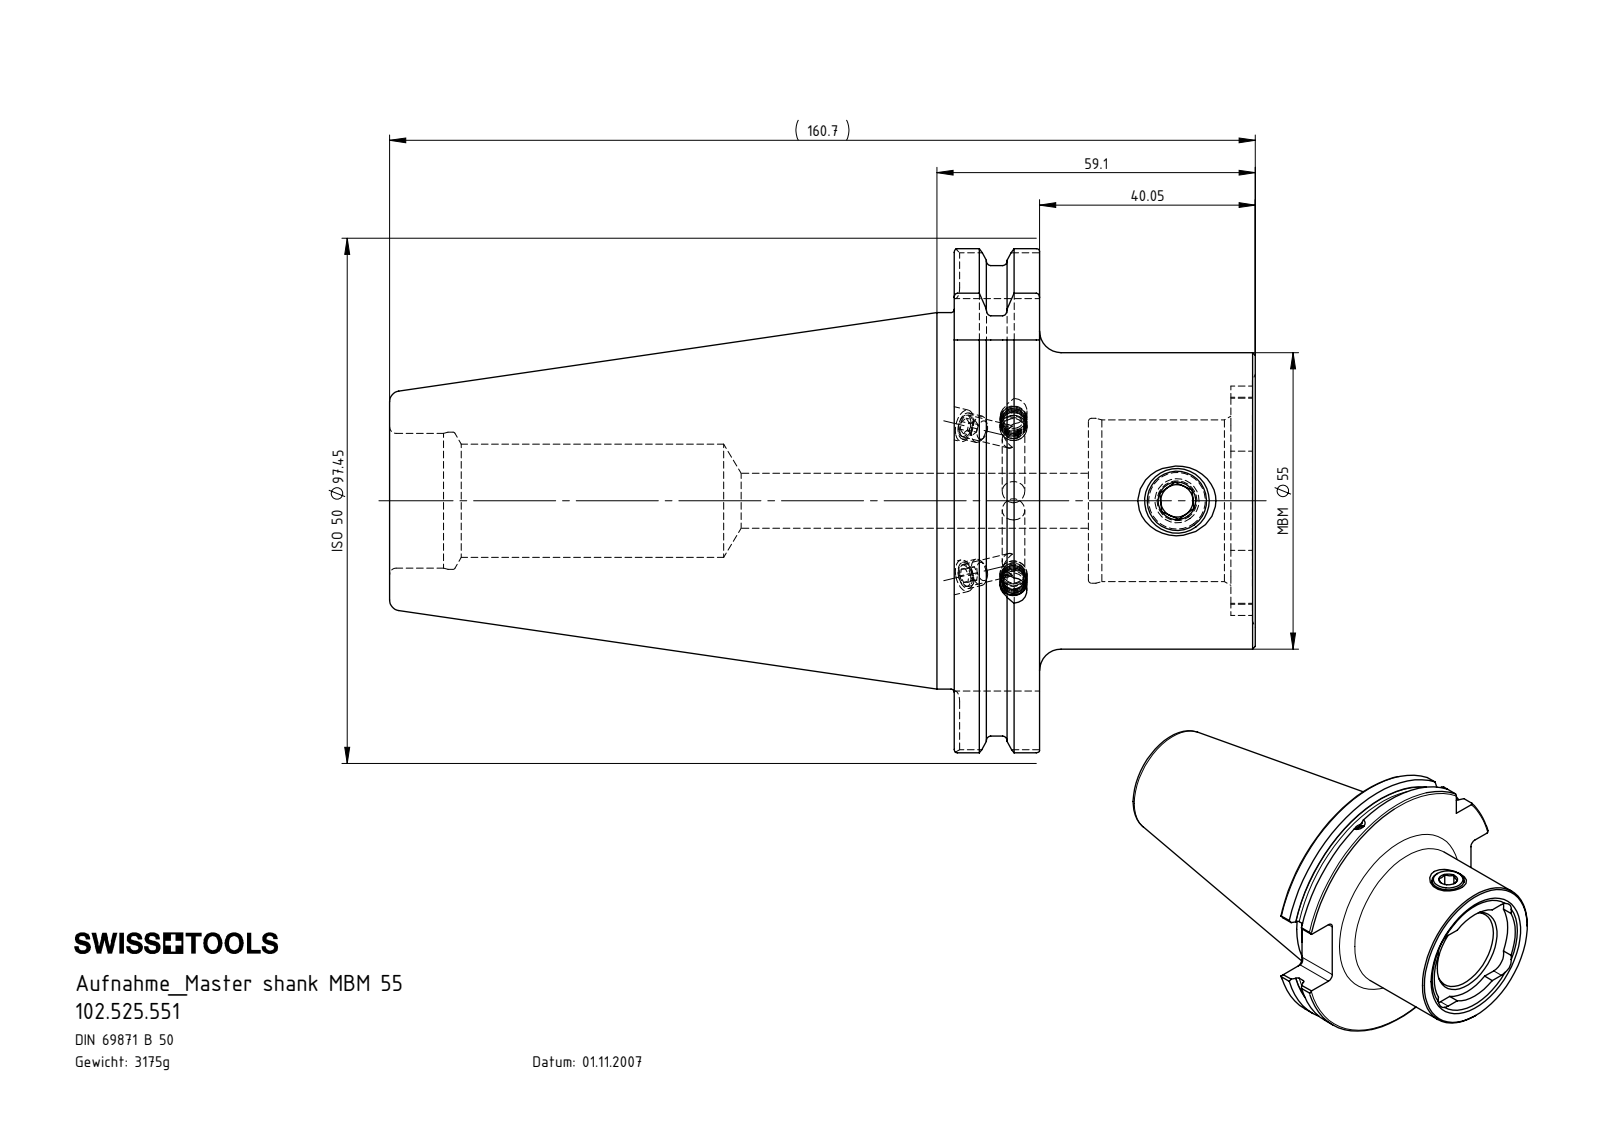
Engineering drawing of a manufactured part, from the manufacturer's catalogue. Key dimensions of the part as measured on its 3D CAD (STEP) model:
Part name (STEP PRODUCT): SB5-MB5.K01.059_C_mit Bundkhlung; ISO 4026 - M5 x 4_PreviewCfg; KVT_MB_600_050; 102.525.551 (+1 more)
STEP written by: SolidWorks 2017 (CONFIG_CONTROL_DESIGN)
Units: millimetres
Bodies: 8 solids, 297 faces (79 planar, 82 cylindrical, 136 other)
Overall size (bounding box): 160.7 × 97.45 × 93.51
Volume: 404 419 mm³ · Surface area: 54 336 mm²
Round holes (diameter × count): ⌀4.2 ×3, ⌀6 ×3, ⌀4 ×2, ⌀5 ×1, ⌀10.2 ×1, ⌀11 ×1, ⌀21 ×1, ⌀25 ×1, ⌀25.45 ×1, ⌀30 ×1, ⌀30.6 ×1
Round bosses / shafts (diameter × count): ⌀5 ×3, ⌀91 ×1, ⌀69.85 ×1, ⌀55 ×1, ⌀12 ×1
Partial cylindrical surfaces — rounded edges, fillets, slot ends (radius × count): R2 ×8, R5.2 ×4, R18.5 ×1, R21.27 ×1, R48.73 ×1
Main face-to-face distances: 15.85, 24.9, 9.05, 55.9, 40.05, 31, 51.35, 35.5, 26.45, 4.55
